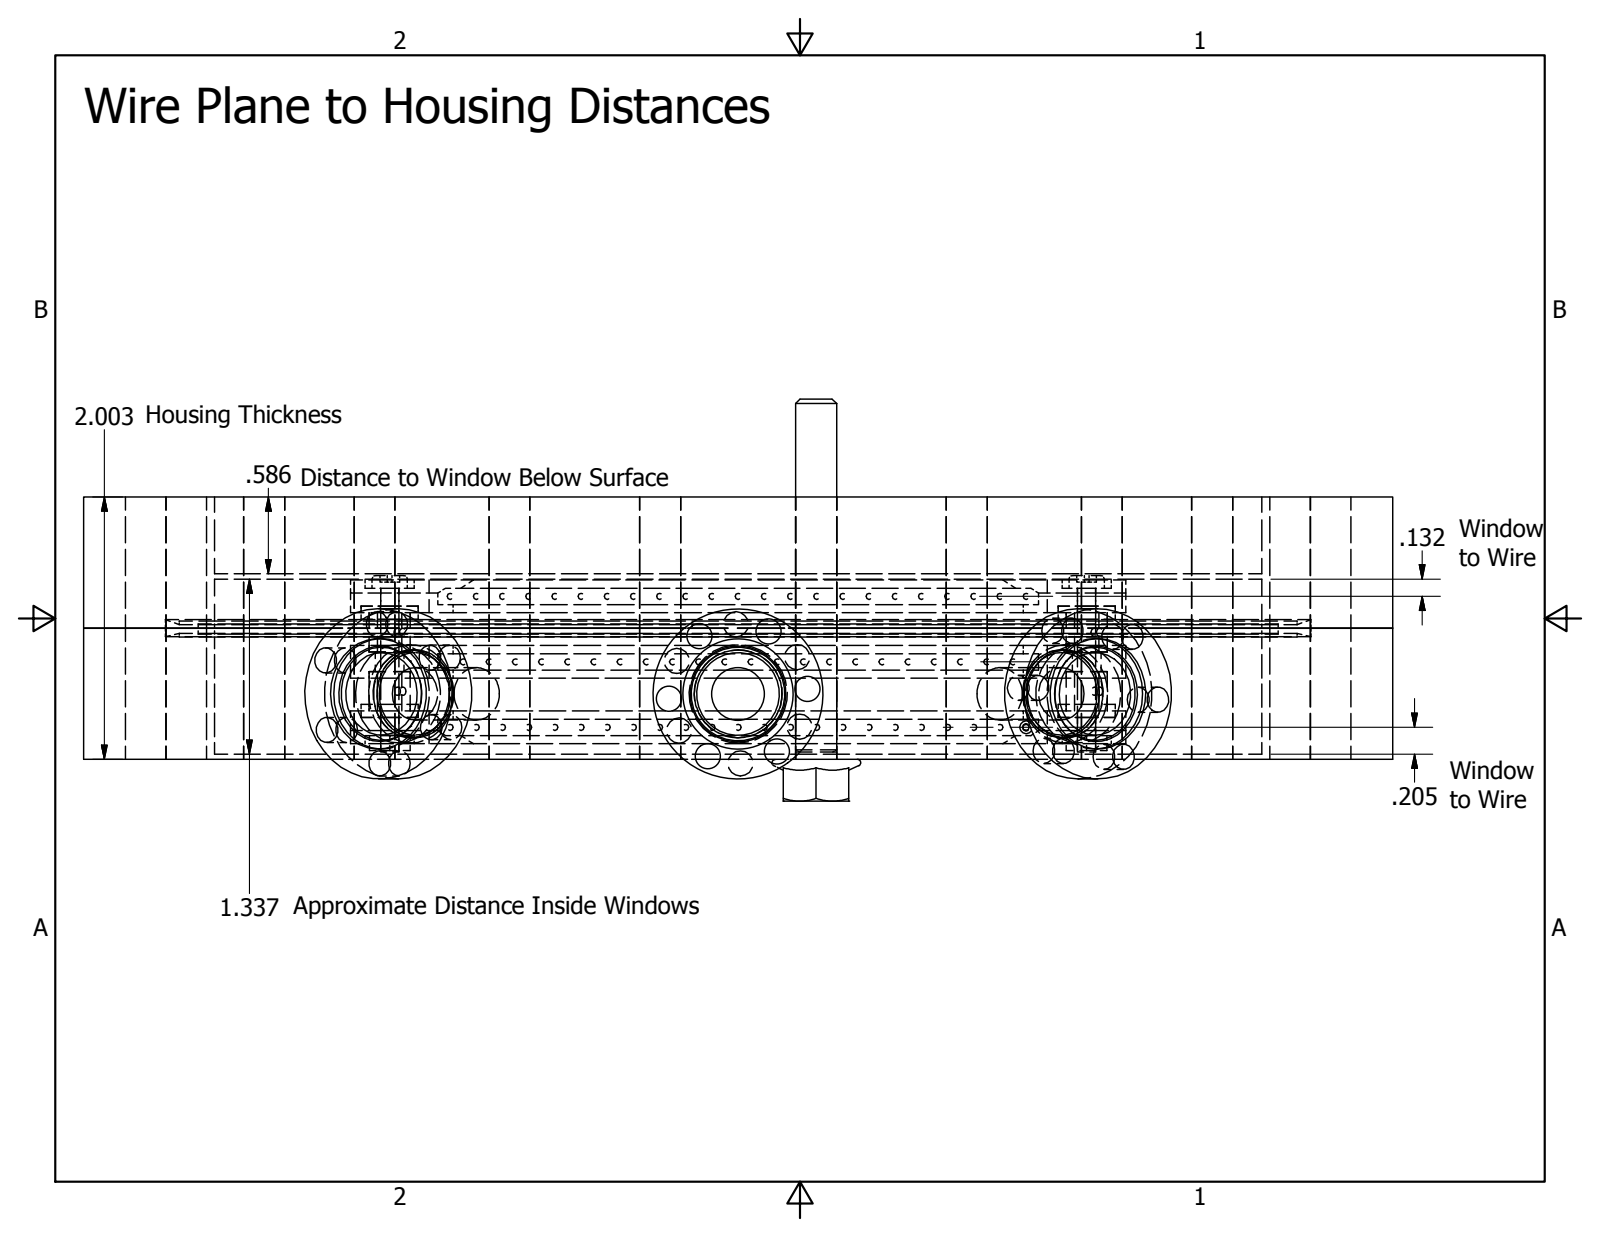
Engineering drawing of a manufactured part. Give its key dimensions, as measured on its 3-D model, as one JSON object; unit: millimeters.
{"part_name": "WindowFlange_Clearance_WithFeedThrough; WeldNeckFeedThrough; WindowFlange_Clearance_NoFeedThrough; IFI 111 - 5_16 x 18 x 2 3_4 (+8 more)", "step_written_by": "Autodesk Inventor 2014 (AUTOMOTIVE_DESIGN)", "units": "millimeters", "bodies": {"solids": 36, "faces": 661, "planar": 282, "cylindrical": 360, "other": 19}, "overall_size": [279.25, 254, 77.98], "volume_mm3": 1081000, "surface_area_mm2": 417251, "round_holes": [[1.19, 68], [7.94, 28], [4.88, 24], [1.59, 8], [3.51, 4], [3.53, 4], [3.56, 4], [4.76, 4], [5.56, 4], [9.52, 4], [11.11, 4], [10.16, 3]], "round_bosses_or_shafts": [[6.86, 4], [33, 3], [19.06, 3], [17.04, 3], [254, 1], [209.55, 1], [2.5, 1], [1.4, 1]], "partial_cylinders_radius": [[3.17, 4]], "face_to_face_distances": [6.35, 25.4, 12.7, 1, 34.96, 33.96, 35.98, 34.98, 1.02, 19.05], "hole_center_spacings": [13.49, 115.92, 30.26, 141.14, 163.94, 214.2, 223.95, 229.86]}
